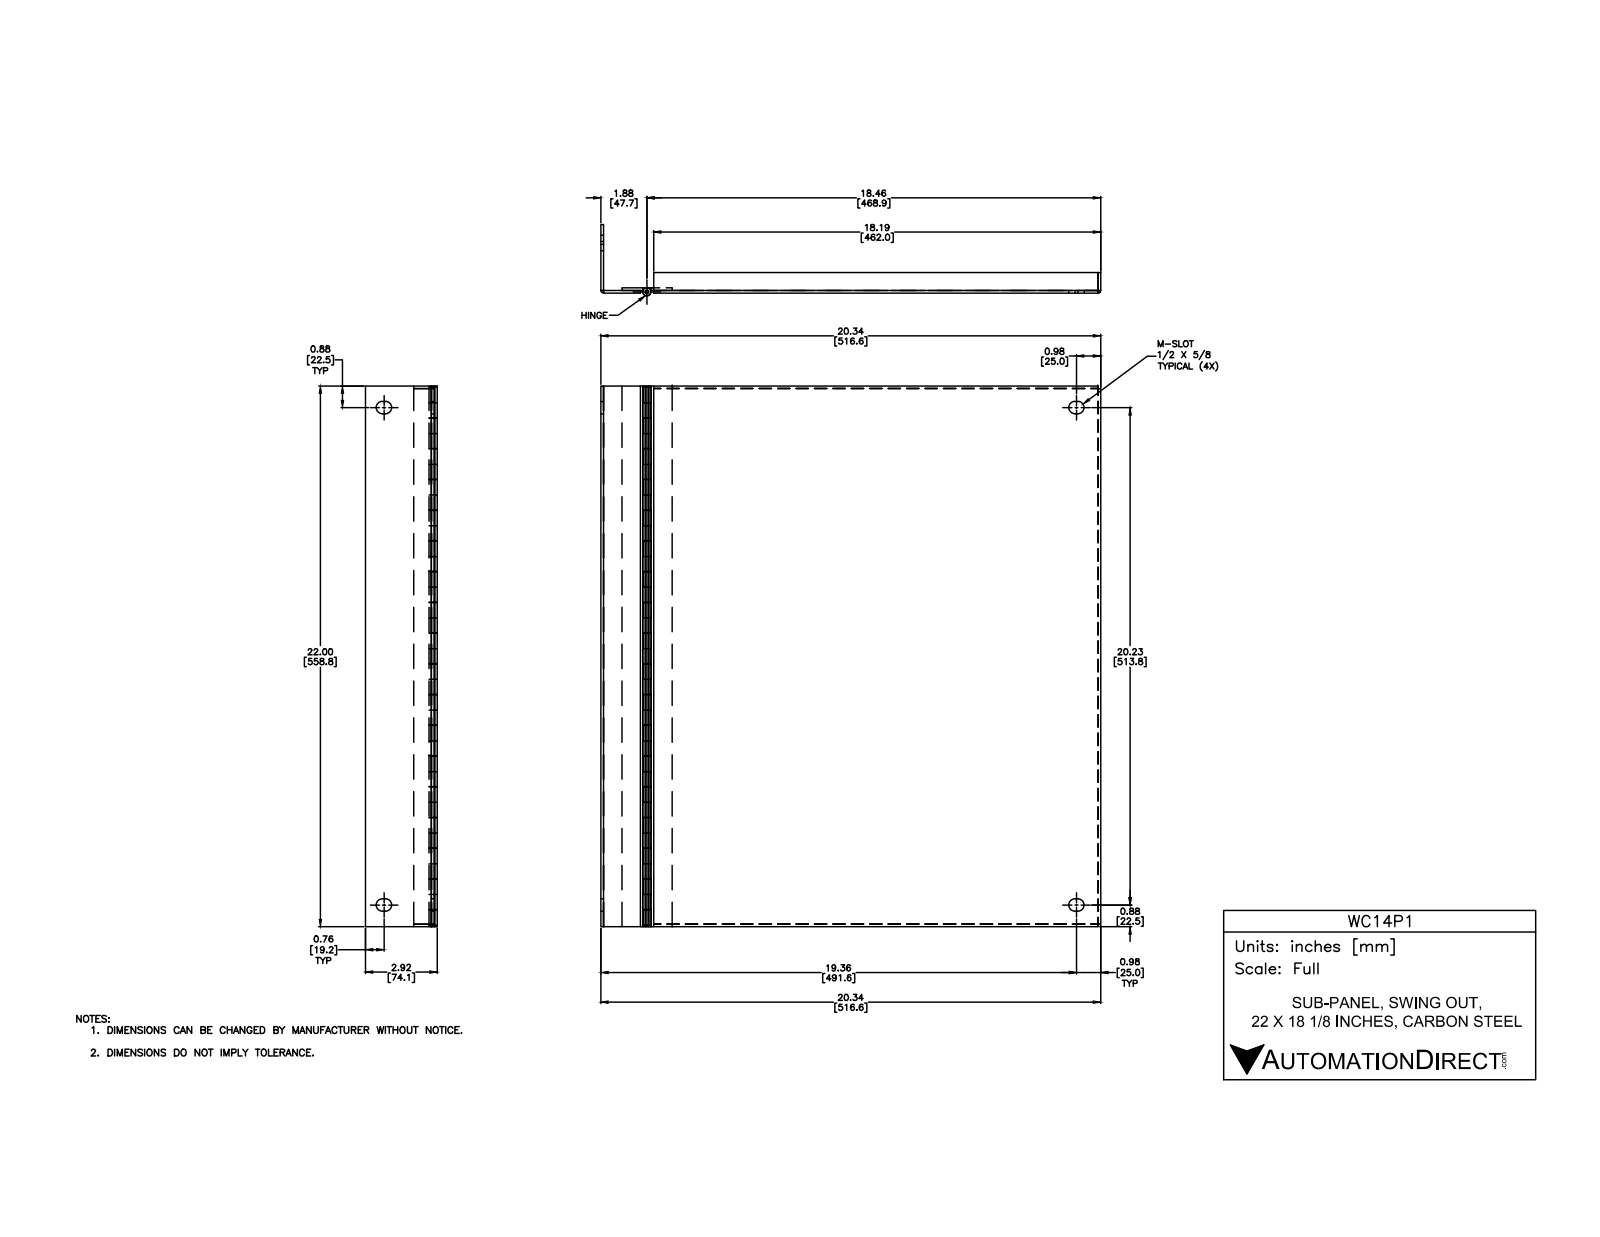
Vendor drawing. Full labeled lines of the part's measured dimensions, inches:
Part name (STEP PRODUCT): WC14P1_HINGEPIN; WC14P1_FLANGE; WC14P1; WC14P1_DOOR (+2 more)
STEP written by: SolidWorks 2014 (AUTOMOTIVE_DESIGN)
Units: inches
Bodies: 5 solids, 294 faces (157 planar, 133 cylindrical, 4 other)
Overall size (bounding box): 22 × 20.338 × 2.917
Volume: 61.71 in³ · Surface area: 1 212 in²
Round holes (diameter × count): ⌀0.145 ×1
Round bosses / shafts (diameter × count): ⌀0.334 ×1, ⌀0.125 ×1
Partial cylindrical surfaces — rounded edges, fillets, slot ends (radius × count): R0.25 ×8, R0.107 ×3, R0.108 ×1
Main face-to-face distances: 0.105, 0.104, 0.209, 21.895, 20.338, 20.233, 20.233, 20.129, 22, 21.791
